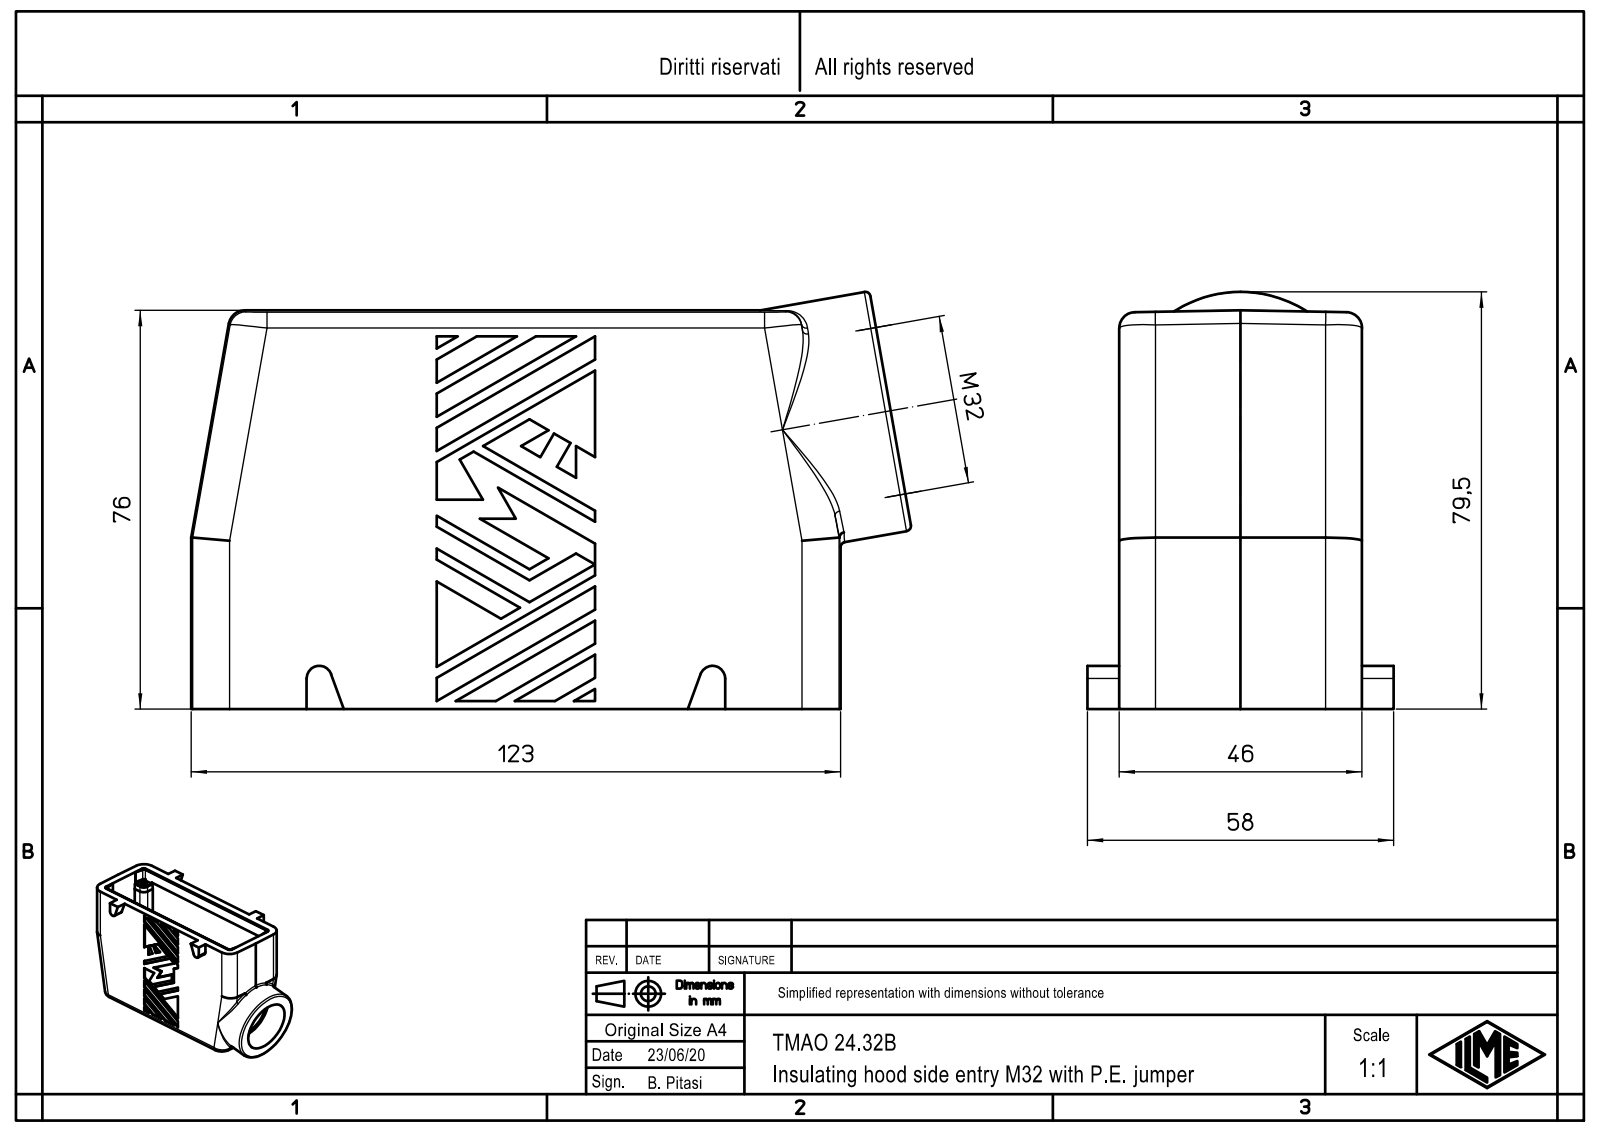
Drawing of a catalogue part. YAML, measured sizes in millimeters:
part_name: "TMAO_24.32B"
step_written_by: "Creo Elements/Direct Modeling 20.1B 02-Apr-2019 (C) Parametric Technology GmbH (AUTOMOTIVE_DESIGN)"
units: millimeters
bodies: {solids: 1, faces: 1277, planar: 1098, cylindrical: 91, other: 88}
overall_size: [136.34, 78.98, 58]
volume: 166189
surface_area: 62347
round_holes:
  - {diameter: 3, count: 4}
  - {diameter: 3.5, count: 4}
  - {diameter: 28, count: 1}
  - {diameter: 32, count: 1}
round_bosses_or_shafts:
  - {diameter: 4.8, count: 4}
  - {diameter: 46, count: 1}
partial_cylinders:
  - {radius: 1.5, count: 14}
  - {radius: 7, count: 8}
  - {radius: 3, count: 6}
  - {radius: 1.3, count: 4}
  - {radius: 1.6, count: 4}
  - {radius: 2, count: 4}
  - {radius: 3.5, count: 4}
  - {radius: 0.36, count: 3}
face_to_face_distances: [46, 0.5, 45.5, 69.99, 5.6, 39.4, 40.2, 5.3, 5.8, 39.7]
hole_center_spacings: [27, 104, 107.45]
